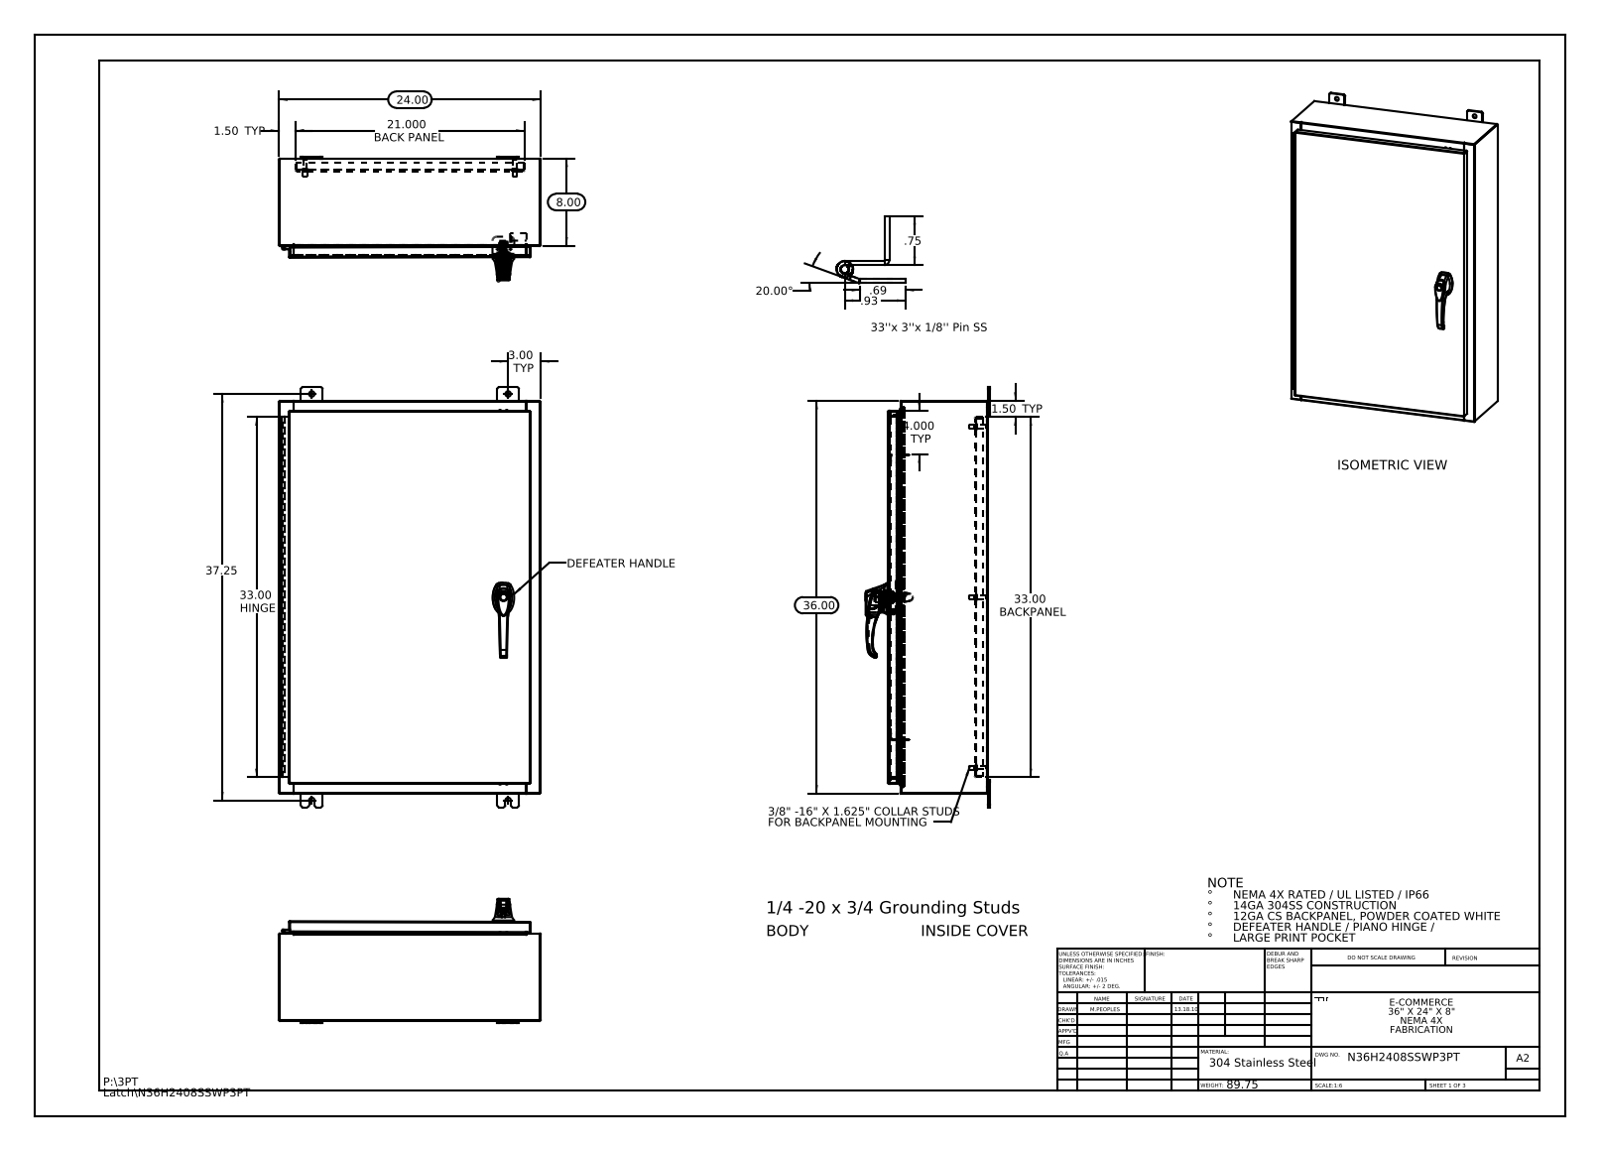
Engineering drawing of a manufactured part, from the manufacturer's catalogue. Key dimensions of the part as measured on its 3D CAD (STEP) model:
Part name (STEP PRODUCT): 022151; N36H2408SSWP3PT Backpanel; Quarter-20 CD Stud; 033060_032151 (+8 more)
STEP written by: SolidWorks 2013 (CONFIG_CONTROL_DESIGN)
Units: inches
Bodies: 39 solids, 2856 faces (1053 planar, 1085 cylindrical, 718 other)
Overall size (bounding box): 38.5 × 24 × 11.495
Volume: 318.5 in³ · Surface area: 7 860 in²
Round holes (diameter × count): ⌀0.5 ×10, ⌀0.25 ×4, ⌀0.138 ×3, ⌀0.161 ×3, ⌀0.079 ×2, ⌀0.203 ×2, ⌀0.313 ×2, ⌀0.437 ×2, ⌀0.125 ×1, ⌀0.125 ×1, ⌀0.197 ×1, ⌀0.276 ×1
Round bosses / shafts (diameter × count): ⌀0.625 ×6, ⌀0.375 ×6, ⌀0.33 ×6, ⌀0.157 ×4, ⌀0.14 ×4, ⌀0.315 ×3, ⌀0.236 ×3, ⌀1.181 ×1
Partial cylindrical surfaces — rounded edges, fillets, slot ends (radius × count): R0.118 ×37, R0.006 ×33, R0.013 ×24, R0.19 ×24, R0.088 ×18, R0.039 ×15, R0.028 ×12, R0.008 ×6
Main face-to-face distances: 0.075, 9.126, 0.104, 9.051, 9.201, 1, 1.075, 8.051, 8.126, 1.179
Hole centre spacings: 11.363, 13.669, 15.625, 24.793, 19.25, 0.295, 0.625, 0.841
